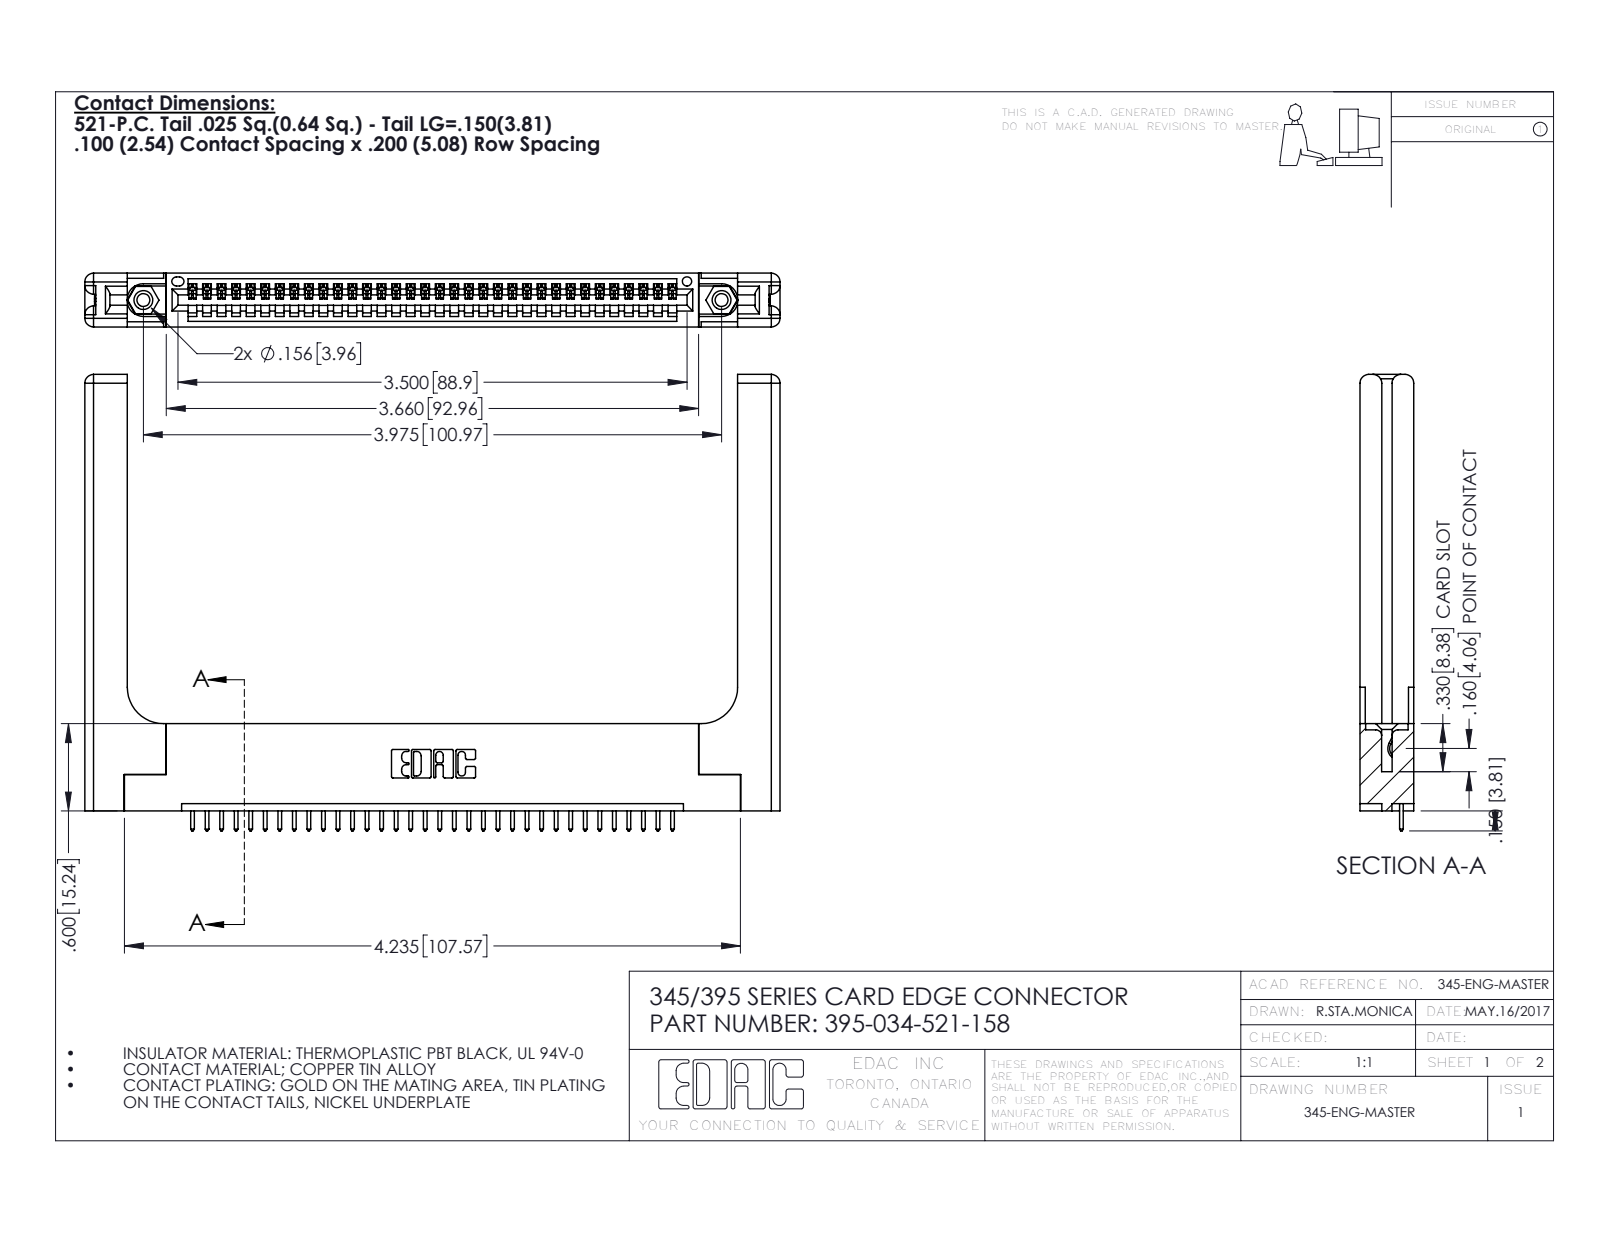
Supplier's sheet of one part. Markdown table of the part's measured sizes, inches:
| quantity | value |
| --- | --- |
| part name | 345 Part_Flush Mounting Lugs - 0.156 Dia-TH; 395-034-521-158; 345-220-058_345-220-058; 345-250-001_345-250-001-102 (+1 more) |
| STEP written by | SolidWorks 2016 (CONFIG_CONTROL_DESIGN) |
| units | inches |
| bodies | 39 solids, 2354 faces (1588 planar, 706 cylindrical, 60 other) |
| overall size | 4.779 × 3.137 × 0.37 |
| volume | 1.213 in³ |
| surface area | 30.88 in² |
| round holes (diameter × count) | 0.089 × 2, 0.125 × 2, 0.156 × 2, 0.064 × 1 |
| round bosses / shafts (diameter × count) | 0.155 × 2 |
| partial cylindrical surfaces (radius × count) | 0.006 × 68, 0.01 × 68, 0.01 × 22, 0.06 × 16, 0.007 × 6, 0.031 × 6, 0.026 × 3, 0.03 × 2 |
| main face-to-face distances | 0.37, 0.072, 0.298, 0.2, 0.098, 0.272, 0.025, 0.148, 0.15, 0.077 |
| hole center spacings | 0.27, 3.74, 3.975 |
